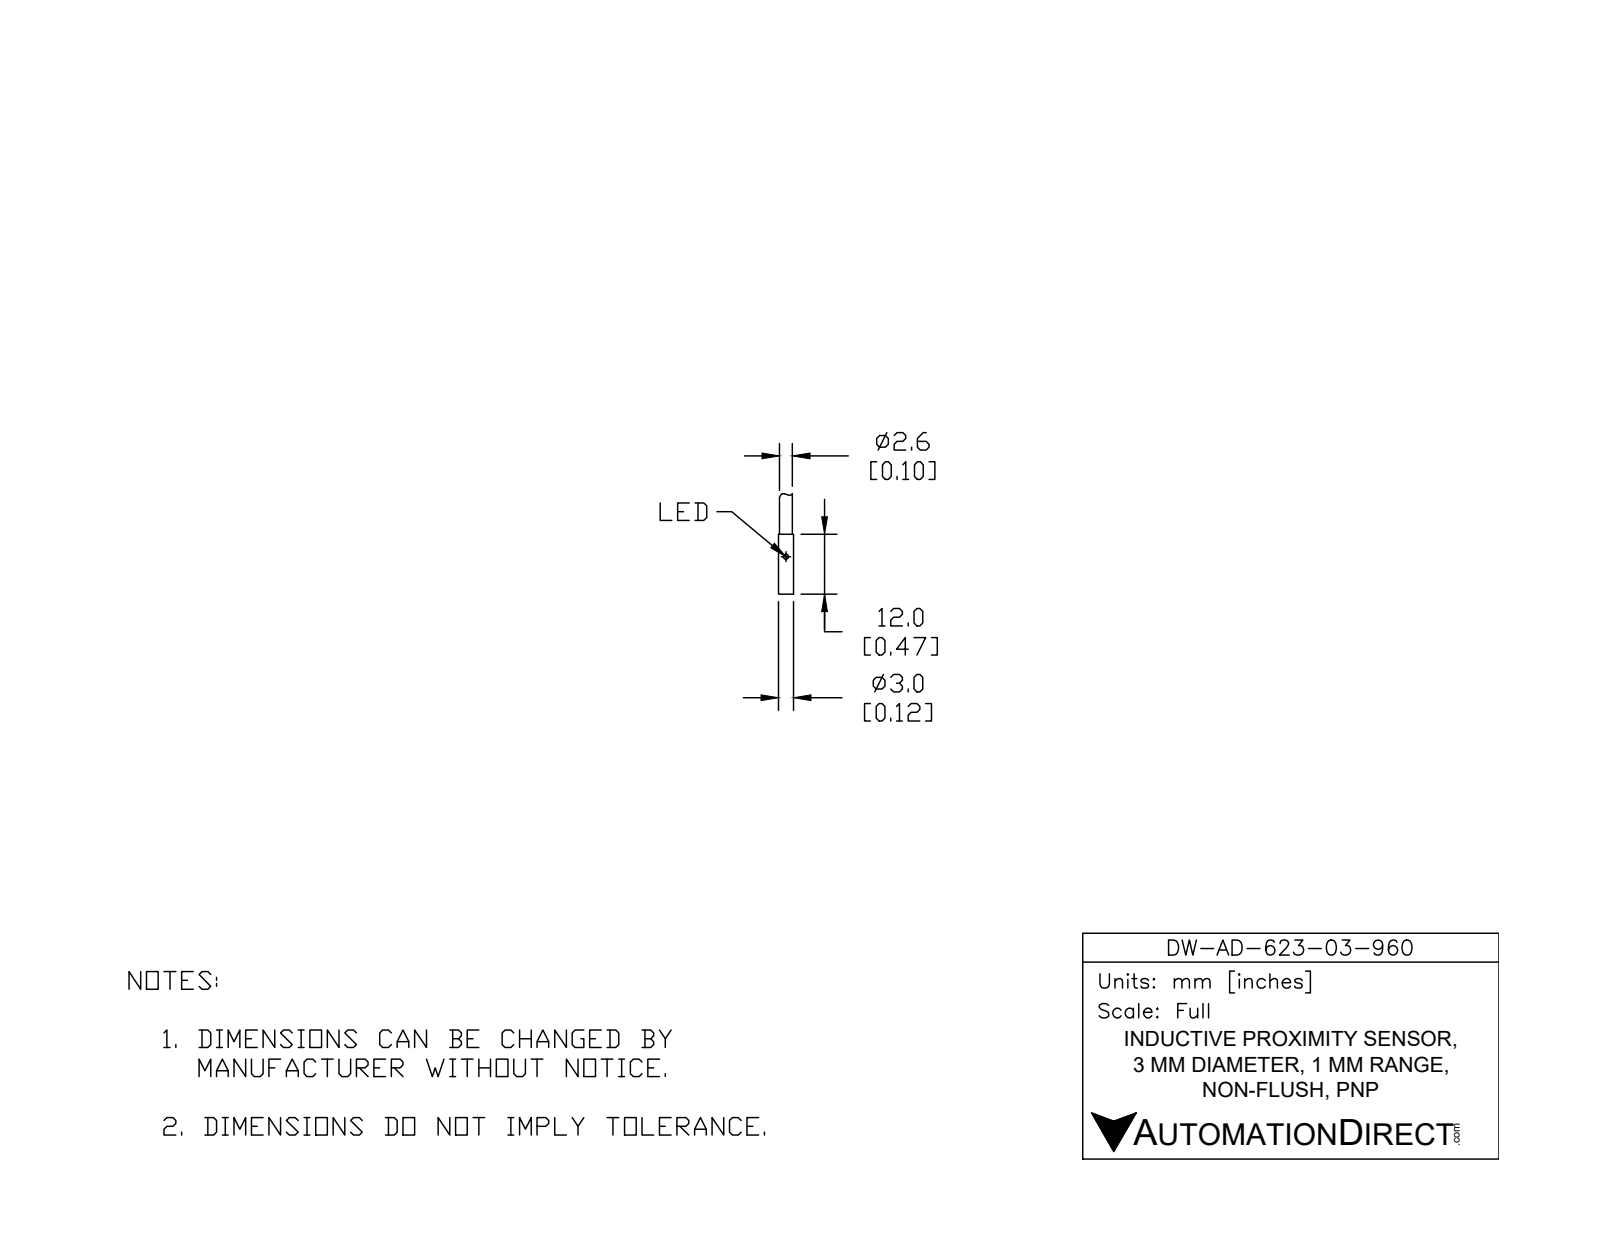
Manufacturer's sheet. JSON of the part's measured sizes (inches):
{"part_name": "DW-AD-623-03-960", "step_written_by": "SolidWorks 2021 (AUTOMOTIVE_DESIGN)", "units": "inches", "bodies": {"solids": 1, "faces": 9, "planar": 5, "cylindrical": 2, "other": 2}, "overall_size": [0.753, 0.118, 0.118], "volume_in3": 0.007, "surface_area_in2": 0.285, "round_bosses_or_shafts": [[0.118, 1], [0.102, 1]], "face_to_face_distances": [0.472]}
